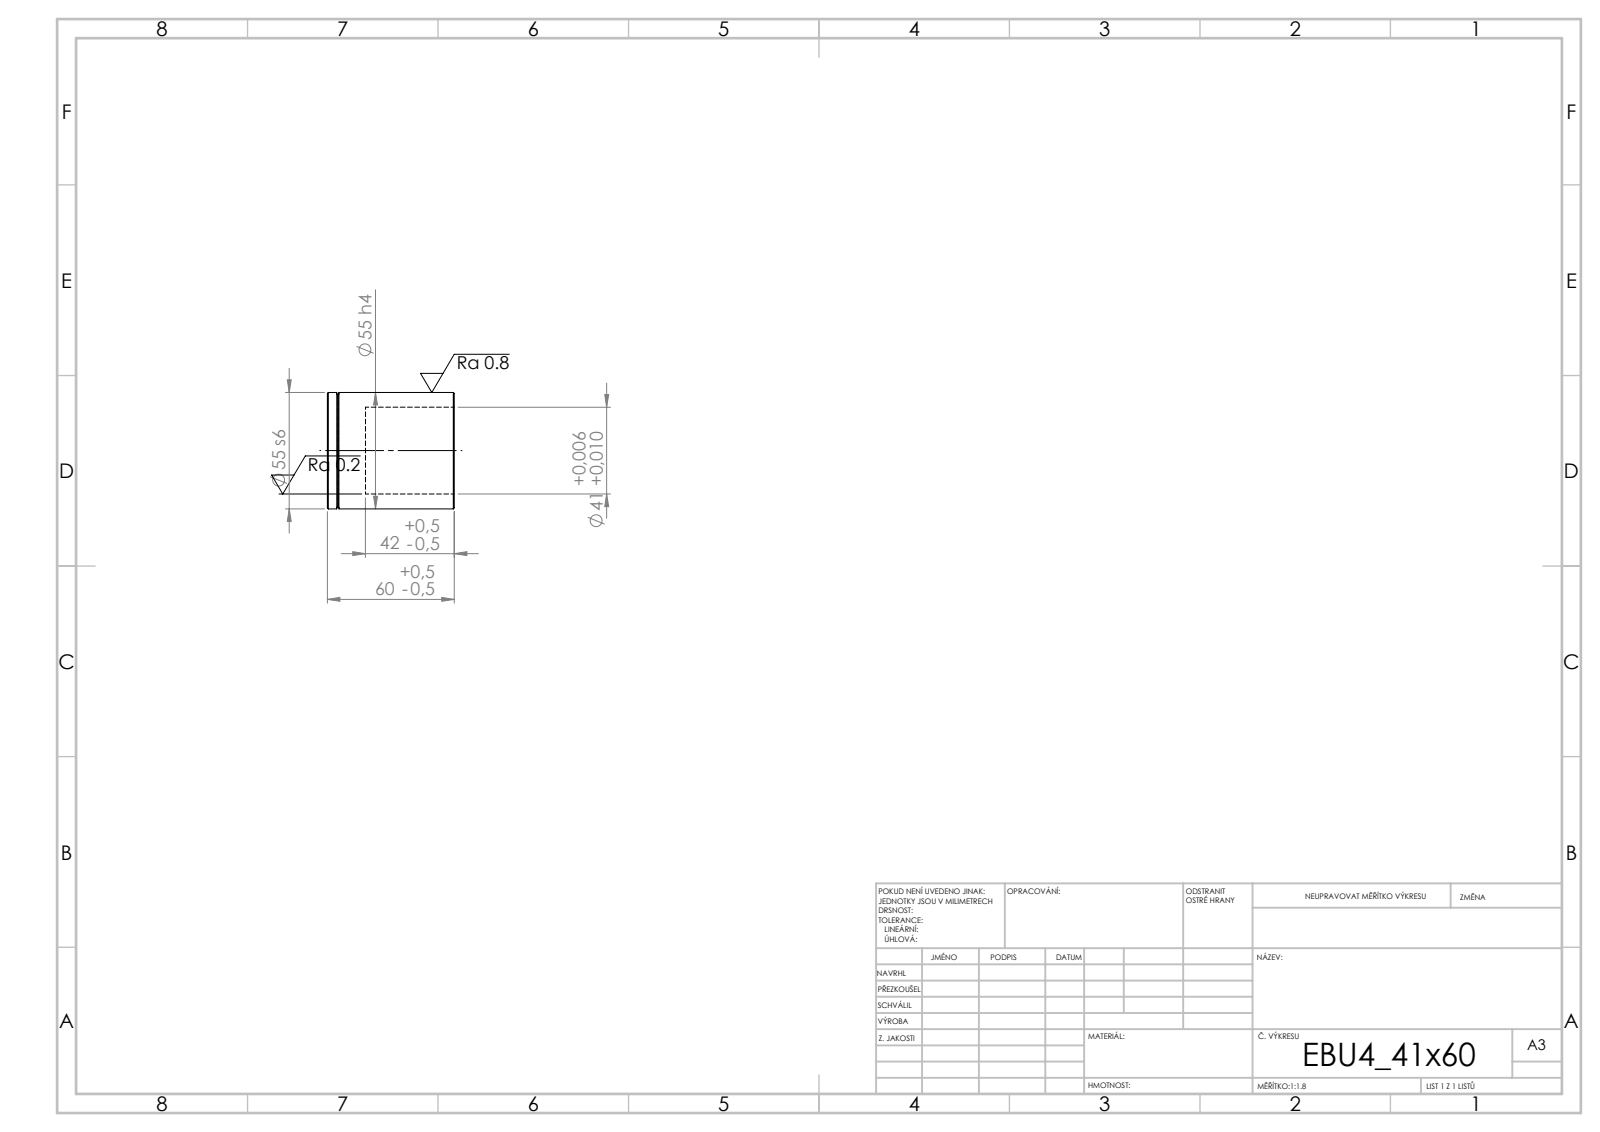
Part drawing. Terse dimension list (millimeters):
written by: SolidWorks 2019 (CONFIG_CONTROL_DESIGN)
unit: mm
bodies: 1 solid, 19 faces (5 planar, 6 cylindrical, 8 other)
size: 60 × 55 × 55
volume: 86 904 mm³; area: 20 689 mm²
holes: 1× ⌀41
bosses: 1× ⌀55
face distances: 18, 42, 60, 55.5, 13.5, 4.5, 54.5, 12.5, 1, 5.5
